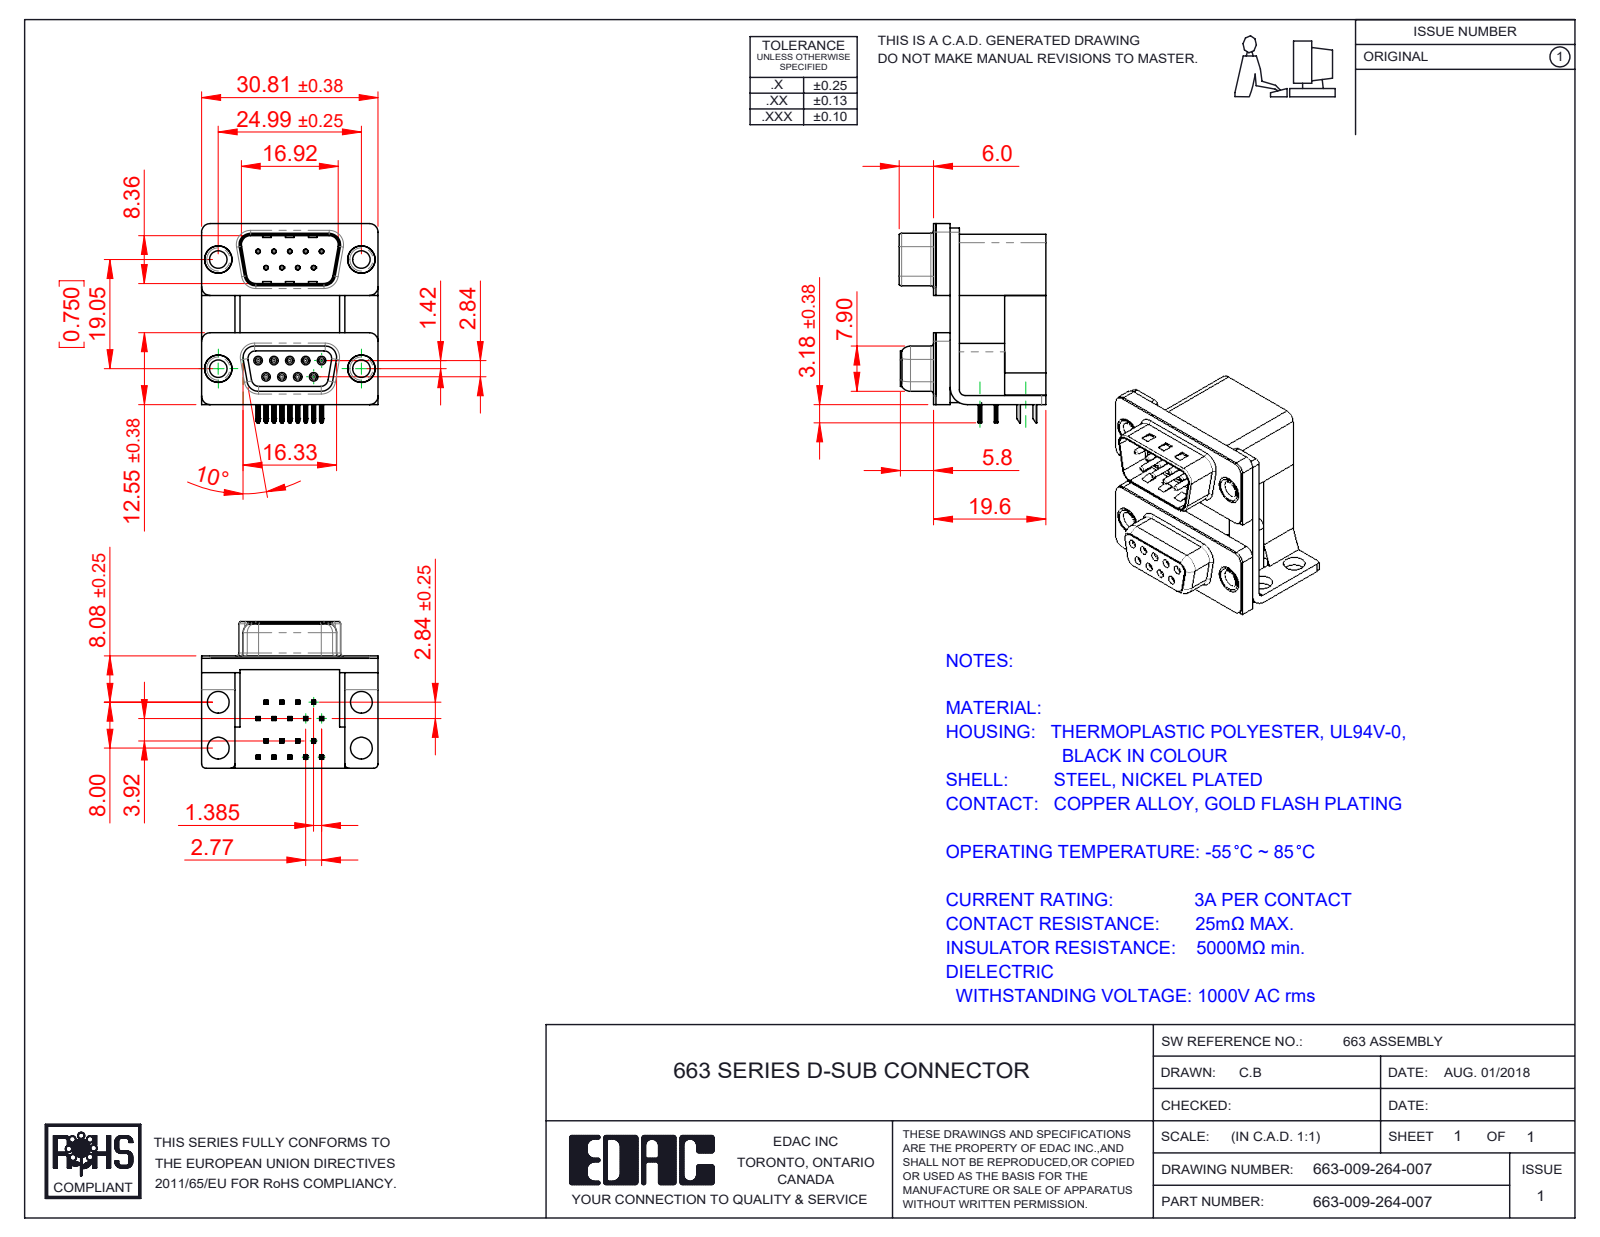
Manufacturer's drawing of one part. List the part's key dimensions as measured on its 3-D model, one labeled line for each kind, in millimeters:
Part name (STEP PRODUCT): 663 Contact Bottom Upper_M; 663 Housing Upper_09 Contacts M; 663 Shell Receptacle_09 Contacts; 663 Contact Bottom Lower (+8 more)
STEP written by: SolidWorks 2020 (CONFIG_CONTROL_DESIGN)
Units: millimetres
Bodies: 29 solids, 2445 faces (1263 planar, 659 cylindrical, 523 other)
Overall size (bounding box): 34.78 × 30.81 × 25.6
Volume: 10 768 mm³ · Surface area: 12 399 mm²
Round holes (diameter × count): ⌀0.8 ×18, ⌀0.35 ×9, ⌀0.9 ×9, ⌀3.05 ×4, ⌀3.5 ×4, ⌀3.8 ×4, ⌀4 ×4, ⌀4.8 ×4, ⌀5 ×4
Round bosses / shafts (diameter × count): ⌀1.2 ×9, ⌀0.75 ×9, ⌀4.9 ×4, ⌀4.75 ×4, ⌀3.85 ×4
Partial cylindrical surfaces — rounded edges, fillets, slot ends (radius × count): R0.1 ×72, R0.15 ×36, R0.25 ×36, R0.12 ×18, R0.35 ×18, R1.5 ×15, R0.5 ×12, R0.34 ×9
Main face-to-face distances: 0.4, 2.5, 16.7, 19.2, 1.6, 7.2, 9.5, 12, 19.6, 12.4
Hole centre spacings: 3.16, 2.77, 19.25, 19.05, 5.54, 19.84, 16.27, 21.93
